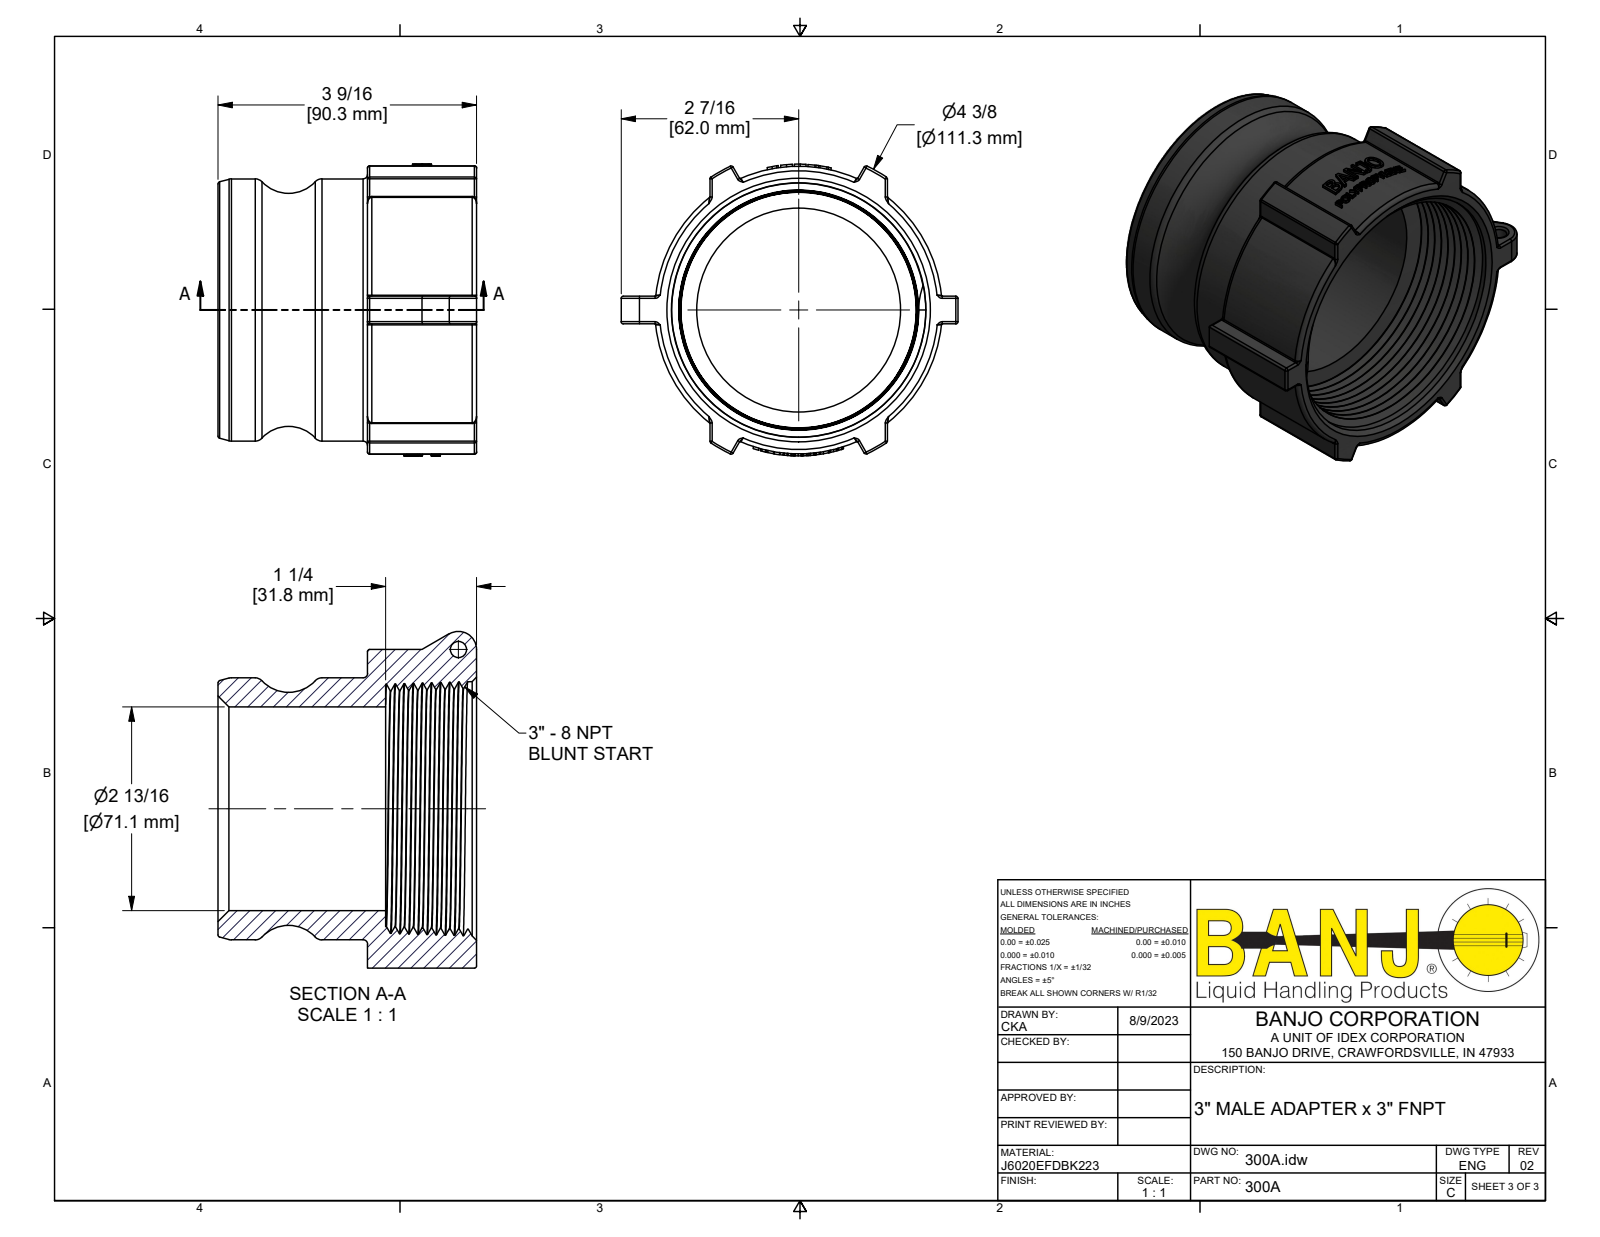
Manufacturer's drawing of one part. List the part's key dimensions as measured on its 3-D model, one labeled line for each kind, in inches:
Part name (STEP PRODUCT): 300A
STEP written by: Autodesk Inventor 2022 (AUTOMOTIVE_DESIGN)
Units: inches
Bodies: 1 solid, 533 faces (179 planar, 104 cylindrical, 250 other)
Overall size (bounding box): 4.63 × 4.01 × 3.555
Volume: 13.36 in³ · Surface area: 100.4 in²
Round holes (diameter × count): ⌀0.22 ×1, ⌀2.8 ×1
Round bosses / shafts (diameter × count): ⌀3.602 ×1
Partial cylindrical surfaces — rounded edges, fillets, slot ends (radius × count): R0.03 ×32, R0.015 ×12, R0.25 ×1, R0.97 ×1, R1.975 ×1, R2.005 ×1, R2.19 ×1
Main face-to-face distances: 2.305, 3.555, 1.25, 0.25, 2.055, 1.5, 0.97, 3.41, 2.44, 0.38
